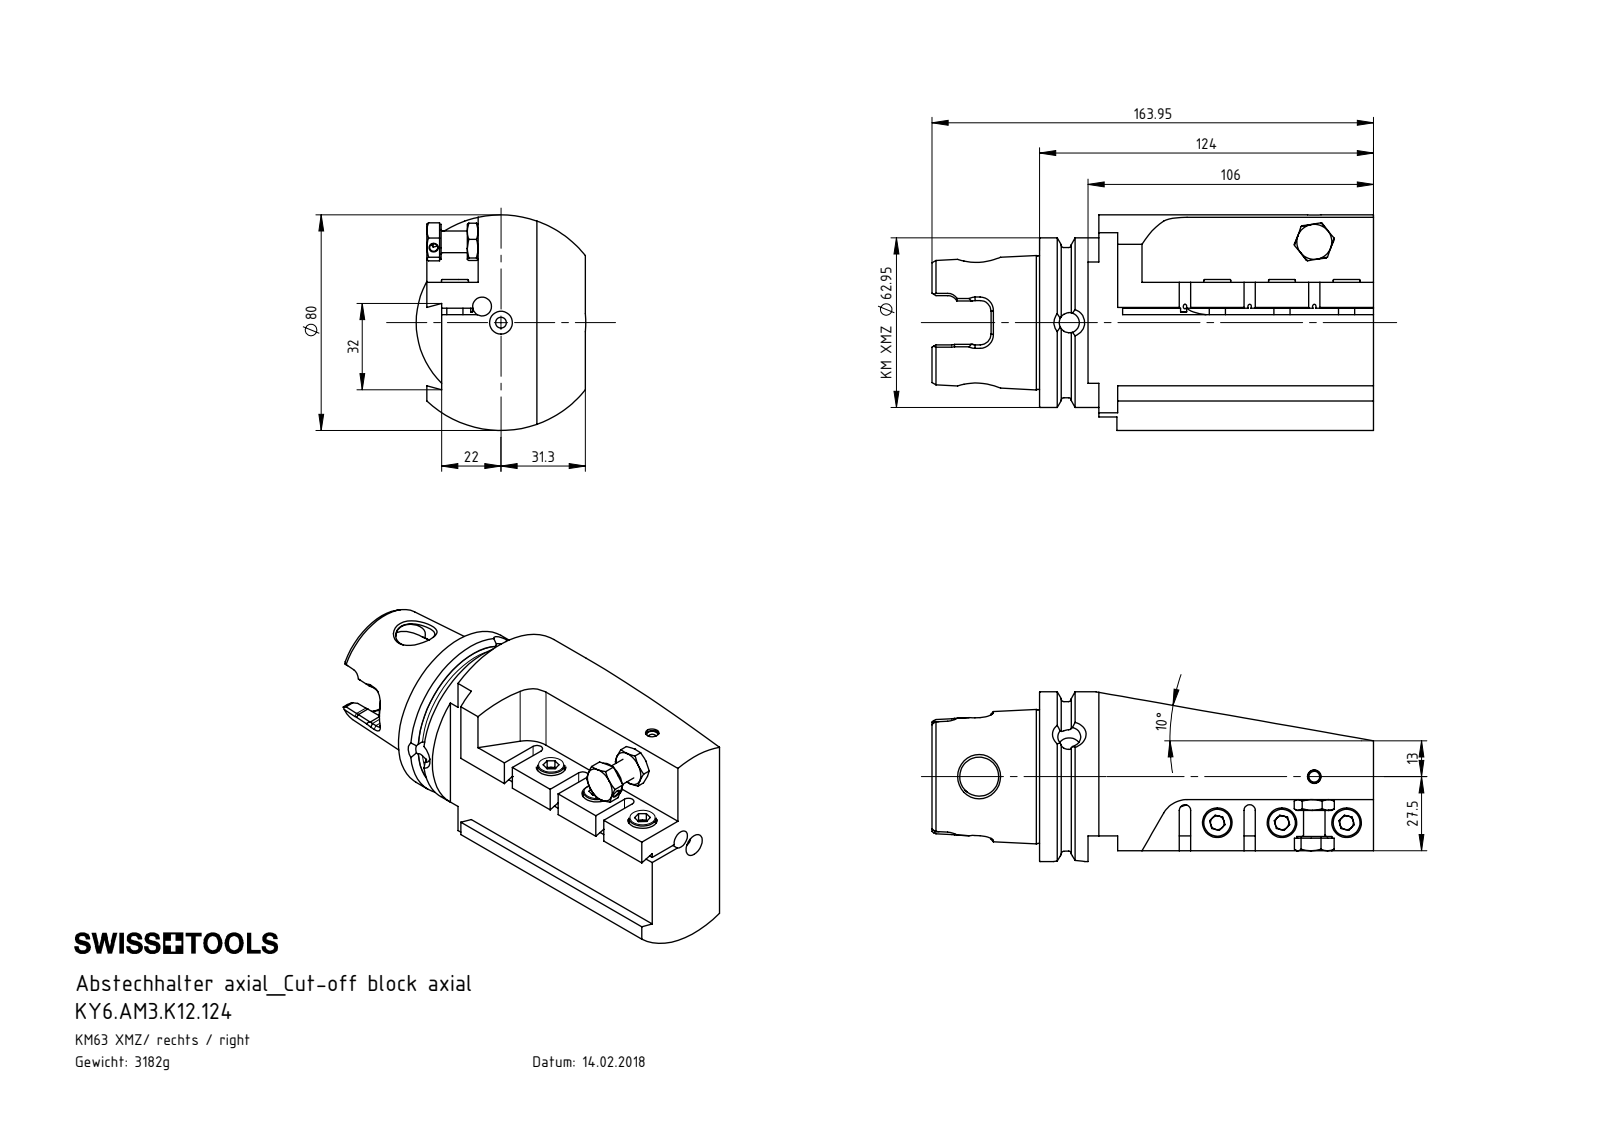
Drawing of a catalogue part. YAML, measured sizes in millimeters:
part_name: "KY6-AM3.K12.124_B; AM3-ER1.001.020_PreviewCfg; ISO 4762 - M6 x 16_PreviewCfg; KY6.AM3.K12.124 (+2 more)"
step_written_by: "SolidWorks 2017 (CONFIG_CONTROL_DESIGN)"
units: millimeters
bodies: {solids: 8, faces: 477, planar: 153, cylindrical: 114, other: 210}
overall_size: [163.95, 80, 62.95]
volume: 406491
surface_area: 59163
round_holes:
  - {diameter: 6.4, count: 4}
  - {diameter: 4, count: 3}
  - {diameter: 4.5, count: 3}
  - {diameter: 11, count: 3}
  - {diameter: 7, count: 2}
  - {diameter: 7.47, count: 2}
  - {diameter: 3, count: 1}
  - {diameter: 4.2, count: 1}
  - {diameter: 6, count: 1}
  - {diameter: 8.48, count: 1}
  - {diameter: 10, count: 1}
  - {diameter: 11.5, count: 1}
round_bosses_or_shafts:
  - {diameter: 10, count: 3}
  - {diameter: 6, count: 3}
  - {diameter: 62.95, count: 1}
  - {diameter: 55.7, count: 1}
  - {diameter: 13, count: 1}
  - {diameter: 8, count: 1}
  - {diameter: 5, count: 1}
partial_cylinders:
  - {radius: 4, count: 6}
  - {radius: 2.1, count: 3}
  - {radius: 7.04, count: 2}
  - {radius: 10, count: 1}
  - {radius: 40, count: 1}
  - {radius: 77.5, count: 1}
face_to_face_distances: [13.5, 19, 5.5, 12, 102, 22, 124, 24, 9.6, 2.4]
hole_center_spacings: [20.89, 24, 9.22, 39.85, 48, 90.04, 95.77, 113.69]
